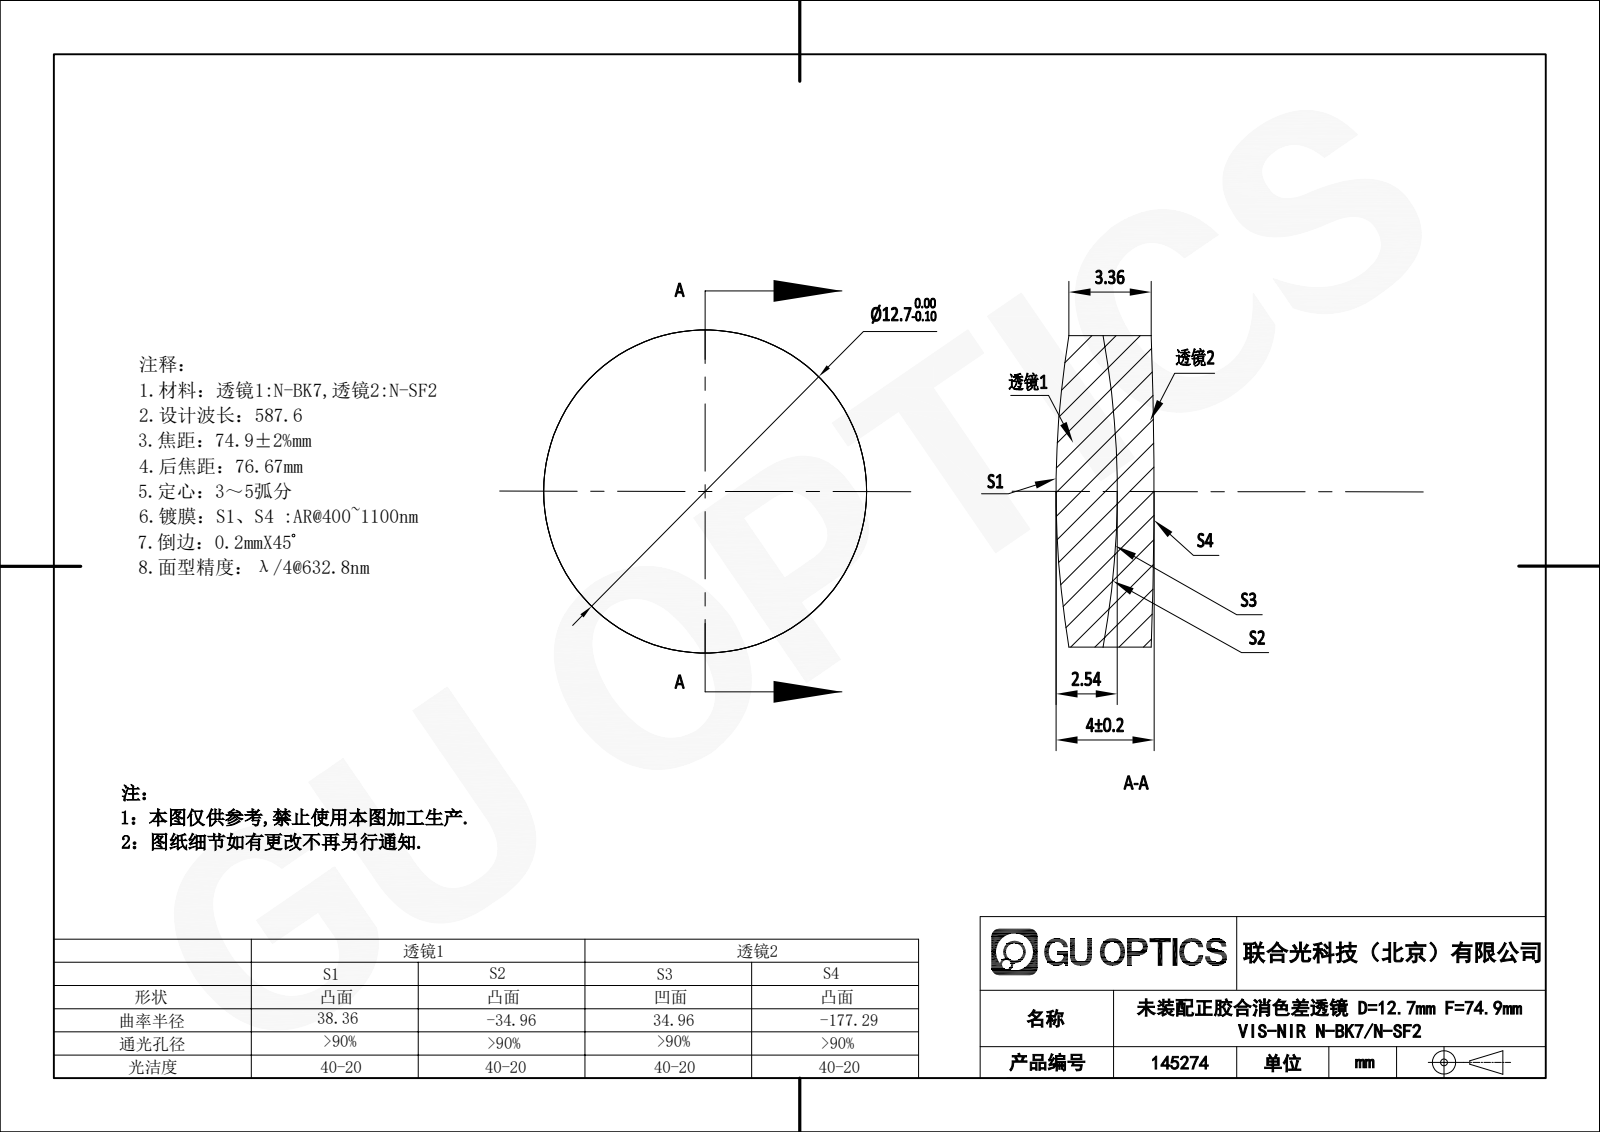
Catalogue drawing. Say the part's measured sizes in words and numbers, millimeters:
The part is named "145274". Its 3-D file was written by "SolidWorks 2020 (CONFIG_CONTROL_DESIGN)". It is 2 solids with 12 faces: 0 planar, 4 cylindrical and 8 other. Overall it measures 12.7 by 12.7 by 4 millimeters. Its volume is 466 cubic millimeters and its surface area 644 square millimeters. Round bosses or shafts: 1 of diameter 12.7.
